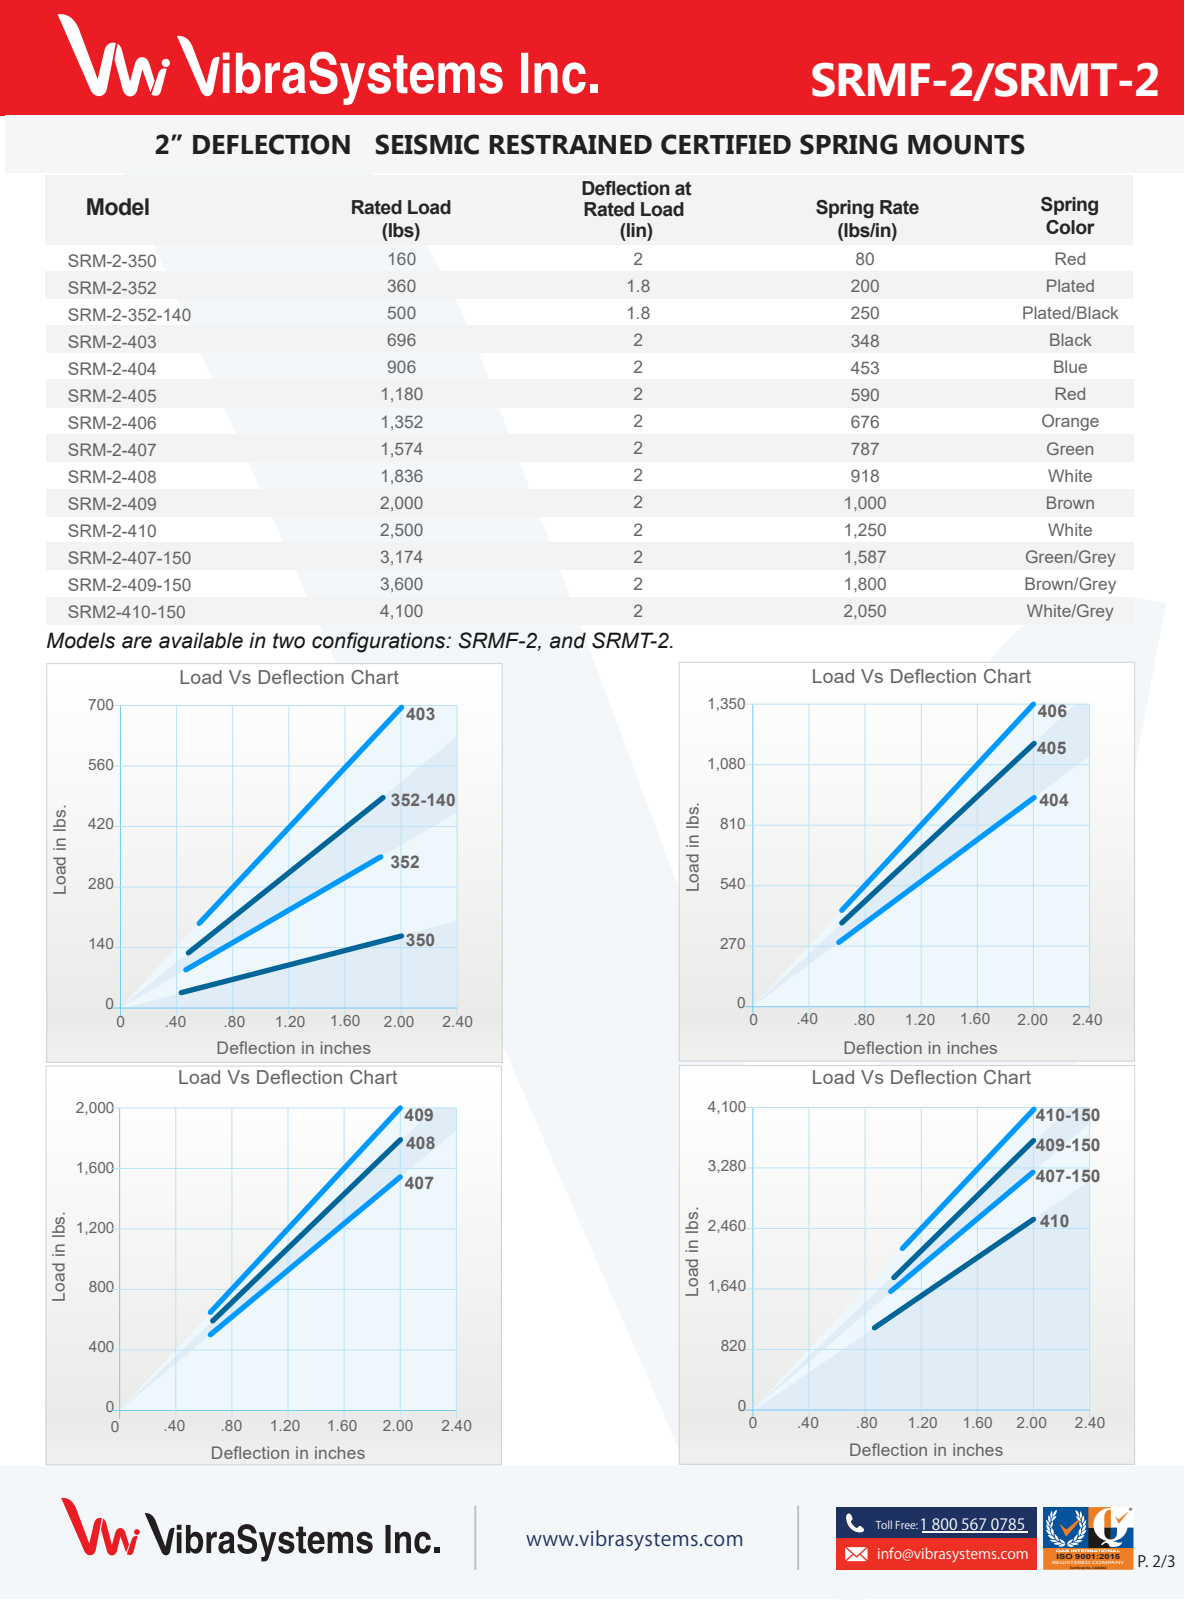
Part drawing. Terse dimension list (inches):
name: SRMT-2-350 Rev N
written by: SolidWorks 2016 (CONFIG_CONTROL_DESIGN)
unit: in
bodies: 1 solid, 313 faces (201 planar, 112 cylindrical, 0 other)
size: 12 × 11 × 8
volume: 250.4 in³; area: 1 044 in²
holes: 4× ⌀0.687
bosses: 4× ⌀0.87, 4× ⌀0.5, 2× ⌀3.54, 2× ⌀3, 2× ⌀1.625, 2× ⌀1.625, 1× ⌀2, 1× ⌀1.75
rounds: 8× R0.112, 8× R0.313, 8× R0.5, 4× R0.75, 2× R0.344
face distances: 0.2, 0.387, 4.587, 0.187, 0.625, 0.587, 7, 4.2, 4, 0.563
hole spacings: 4, 10.25, 11.002
